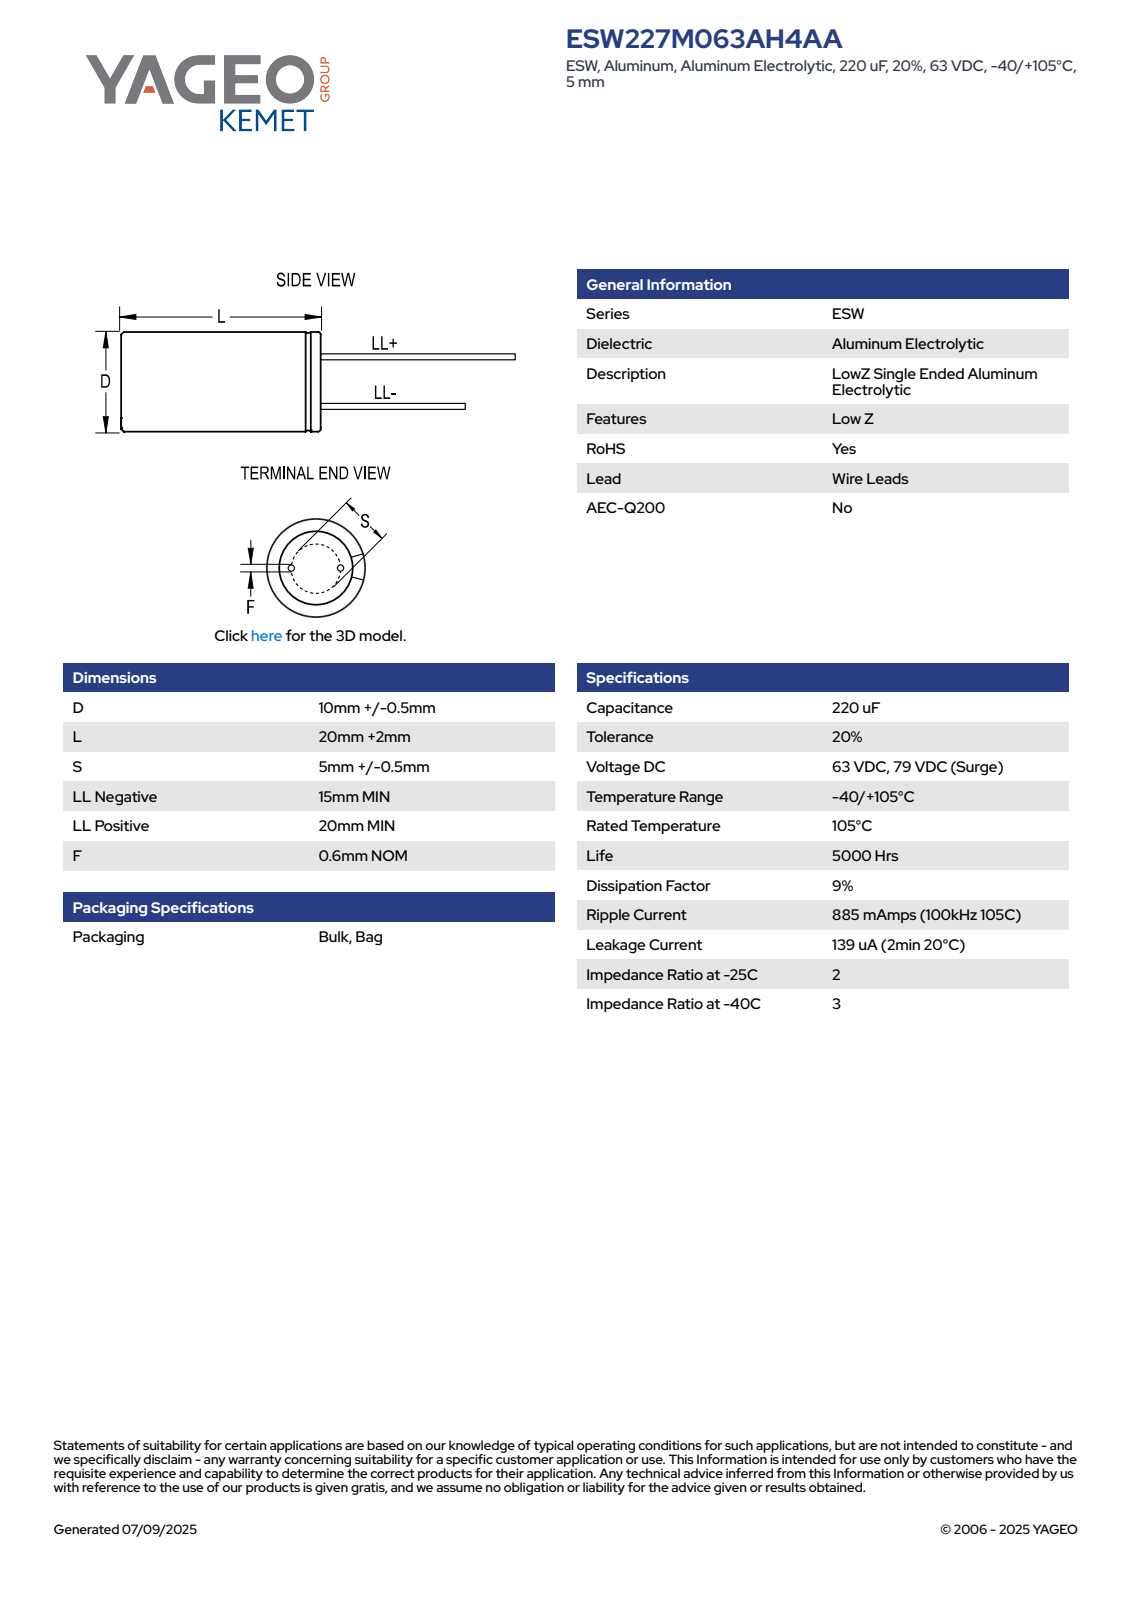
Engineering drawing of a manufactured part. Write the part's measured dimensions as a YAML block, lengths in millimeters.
part_name: "CAR_KLP_10X20_D10.5L22S5F0.6"
step_written_by: "SolidWorks 2014 (AUTOMOTIVE_DESIGN)"
units: millimeters
bodies: {solids: 4, faces: 75, planar: 61, cylindrical: 8, other: 6}
overall_size: [42.01, 10.5, 10.5]
volume: 1903
surface_area: 989
round_bosses_or_shafts:
  - {diameter: 0.6, count: 2}
  - {diameter: 10.5, count: 1}
face_to_face_distances: [22, 22.01, 37.01, 42.01, 37, 42, 15, 20, 5, 1.41]
